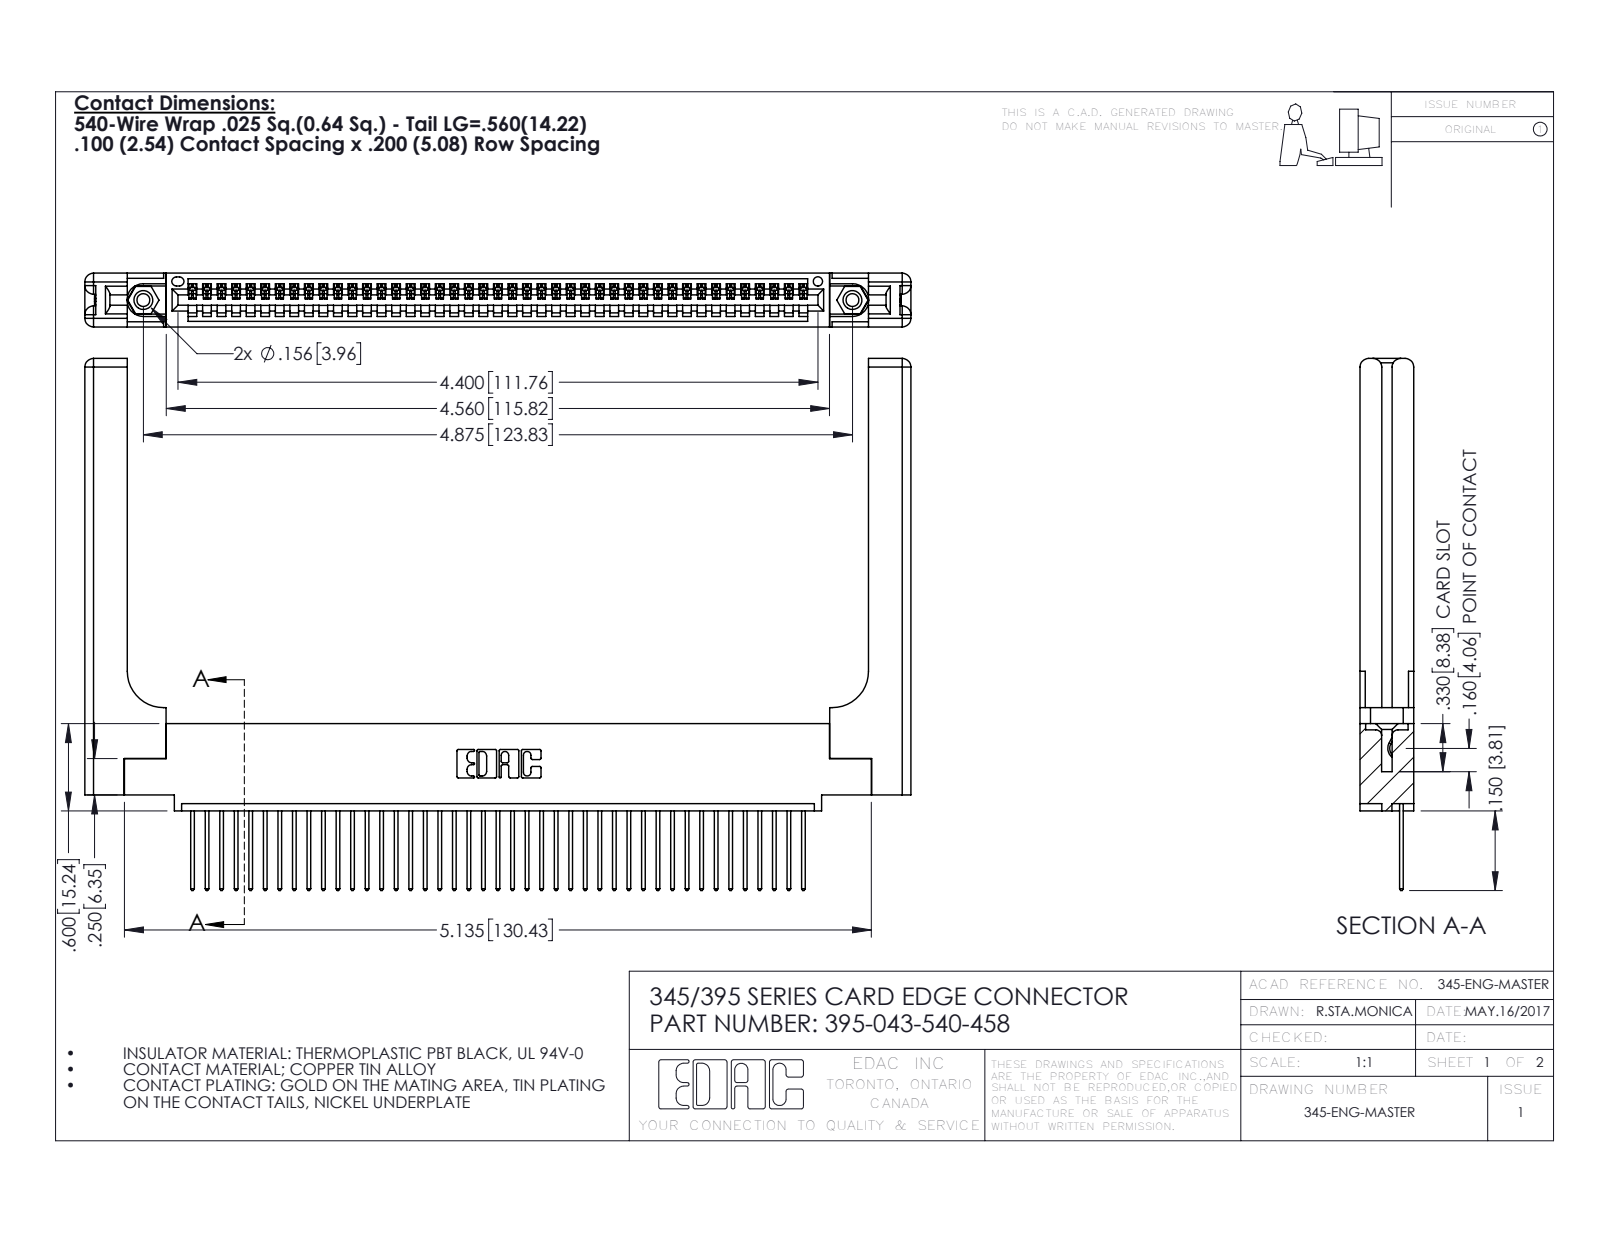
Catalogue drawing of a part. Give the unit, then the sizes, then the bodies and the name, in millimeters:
Units: millimetres
Overall size (bounding box): 144.2 × 92.9 × 9.4
Round holes (diameter × count): ⌀2.3 ×2, ⌀3.2 ×2, ⌀4 ×2, ⌀1.6 ×1
Round bosses / shafts (diameter × count): ⌀3.9 ×2
Partial cylindrical surfaces — rounded edges, fillets, slot ends (radius × count): R0.2 ×86, R0.3 ×86, R0.3 ×22, R1.5 ×16, R0.2 ×6, R0.8 ×6, R0.7 ×3, R0.8 ×2
Main face-to-face distances: 1.8, 9.4, 7.6, 2.5, 6.9, 0.6, 5.1, 5.7, 3.8, 3.8
Hole centre spacings: 6.9, 117.8, 123.8
Volume: 22 200 mm³ · Surface area: 24 020 mm²
Bodies: 48 solids, 2880 faces (1952 planar, 868 cylindrical, 60 other)
Part name (STEP PRODUCT): 345-250-001_345-250-001-102; 395-043-540-458; 345-220-058_345-220-058; 345 Part_0.110 Offset - 0.156 Dia-TH (+1 more)
STEP written by: SolidWorks 2016 (CONFIG_CONTROL_DESIGN)
